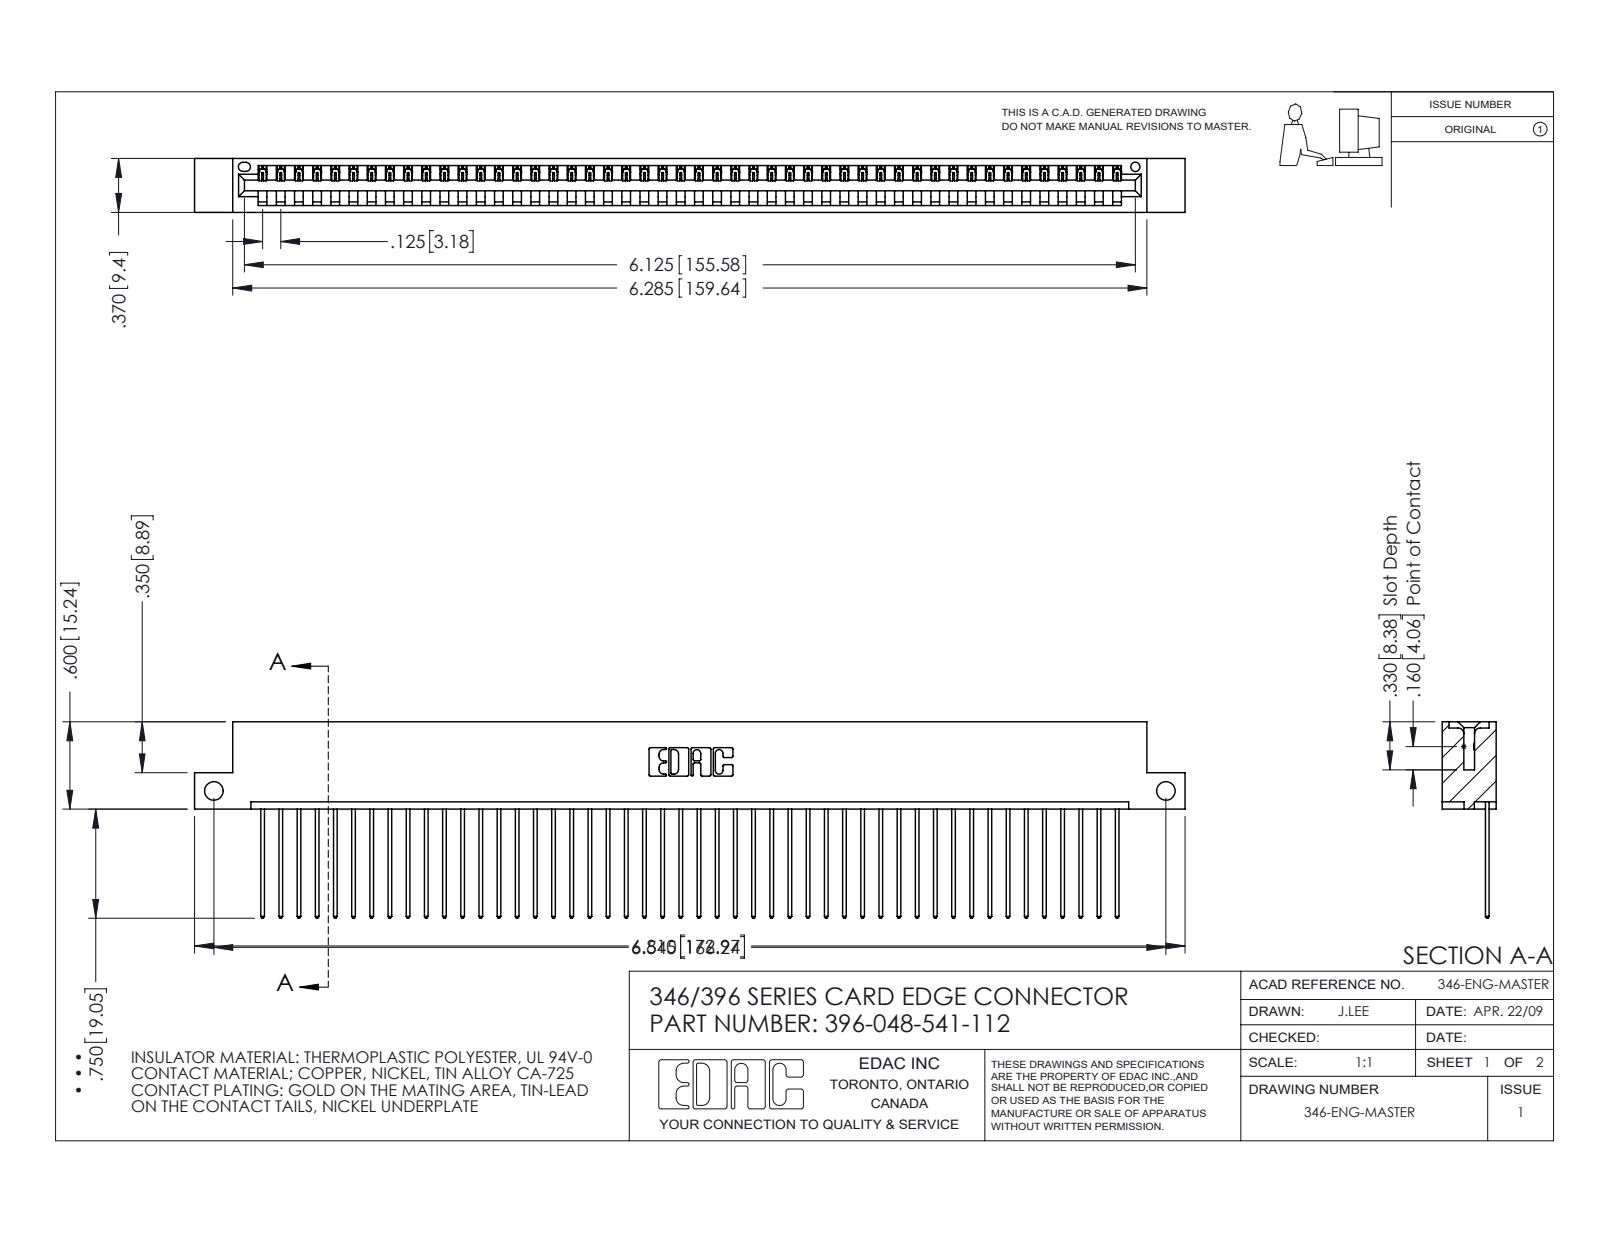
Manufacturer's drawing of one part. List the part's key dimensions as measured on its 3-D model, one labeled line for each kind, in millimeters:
Part name (STEP PRODUCT): 345-292-001_345-293-141; 396-048-541-112; 346 Part_Flush Mounting Lugs - Side Mount
STEP written by: SolidWorks 2016 (CONFIG_CONTROL_DESIGN)
Units: millimetres
Bodies: 49 solids, 2906 faces (1996 planar, 910 cylindrical, 0 other)
Overall size (bounding box): 173 × 34.3 × 9.4
Volume: 16 670 mm³ · Surface area: 21 700 mm²
Round holes (diameter × count): ⌀3.3 ×2, ⌀1.6 ×1
Partial cylindrical surfaces — rounded edges, fillets, slot ends (radius × count): R0.2 ×96, R0.3 ×96, R0.3 ×22, R0.2 ×6, R0.8 ×6, R0.7 ×3, R0.8 ×2, R1 ×2
Main face-to-face distances: 1.2, 8.2, 9.4, 6.4, 1.8, 7.6, 0.6, 3.8, 5.6, 2.5
Hole centre spacings: 166.2
